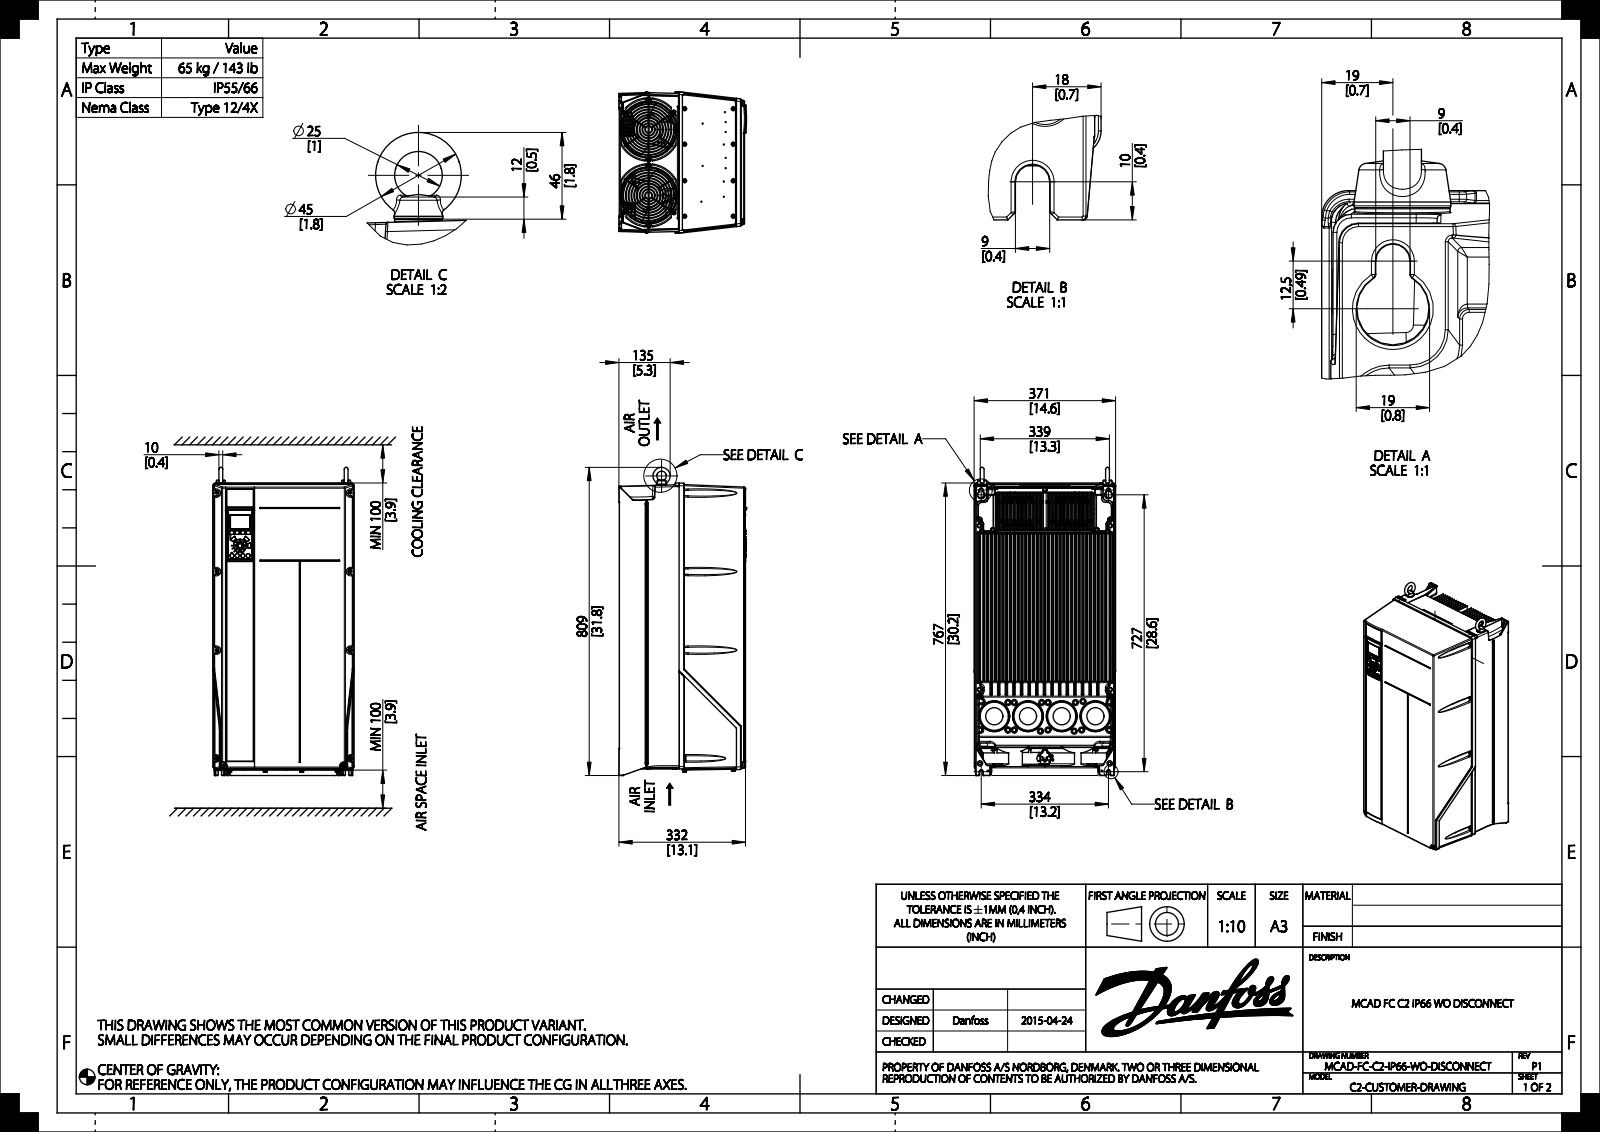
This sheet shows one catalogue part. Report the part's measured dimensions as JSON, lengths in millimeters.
{"part_name": "DANFOSS-FC100-C2-008", "step_written_by": "CREO PARAMETRIC BY PTC INC, 2018070 (CONFIG_CONTROL_DESIGN)", "units": "millimeters", "bodies": {"solids": 1, "faces": 6834, "planar": 1660, "cylindrical": 2550, "other": 2624}, "overall_size": [767.48, 371.37, 335], "volume_mm3": 67720000, "surface_area_mm2": 4073000, "round_holes": [[4.2, 29], [5.5, 20], [4.6, 10], [4.7, 10], [4.55, 8], [2, 3], [3.5, 3], [6, 2], [12, 1]], "round_bosses_or_shafts": [[5, 27], [10, 18], [8.4, 10], [4.4, 10], [2.3, 9], [8.5, 8], [8, 8], [4.48, 8]], "partial_cylinders_radius": [[1, 254], [0.5, 128], [2.5, 101], [0.8, 89], [3, 87], [0.3, 81], [0.7, 79], [0.75, 75]], "face_to_face_distances": [20, 40, 60, 80, 100, 120, 140, 160, 180, 200], "hole_center_spacings": [189, 93, 127.5, 157.81, 96, 159.6, 227.98, 227.99]}
